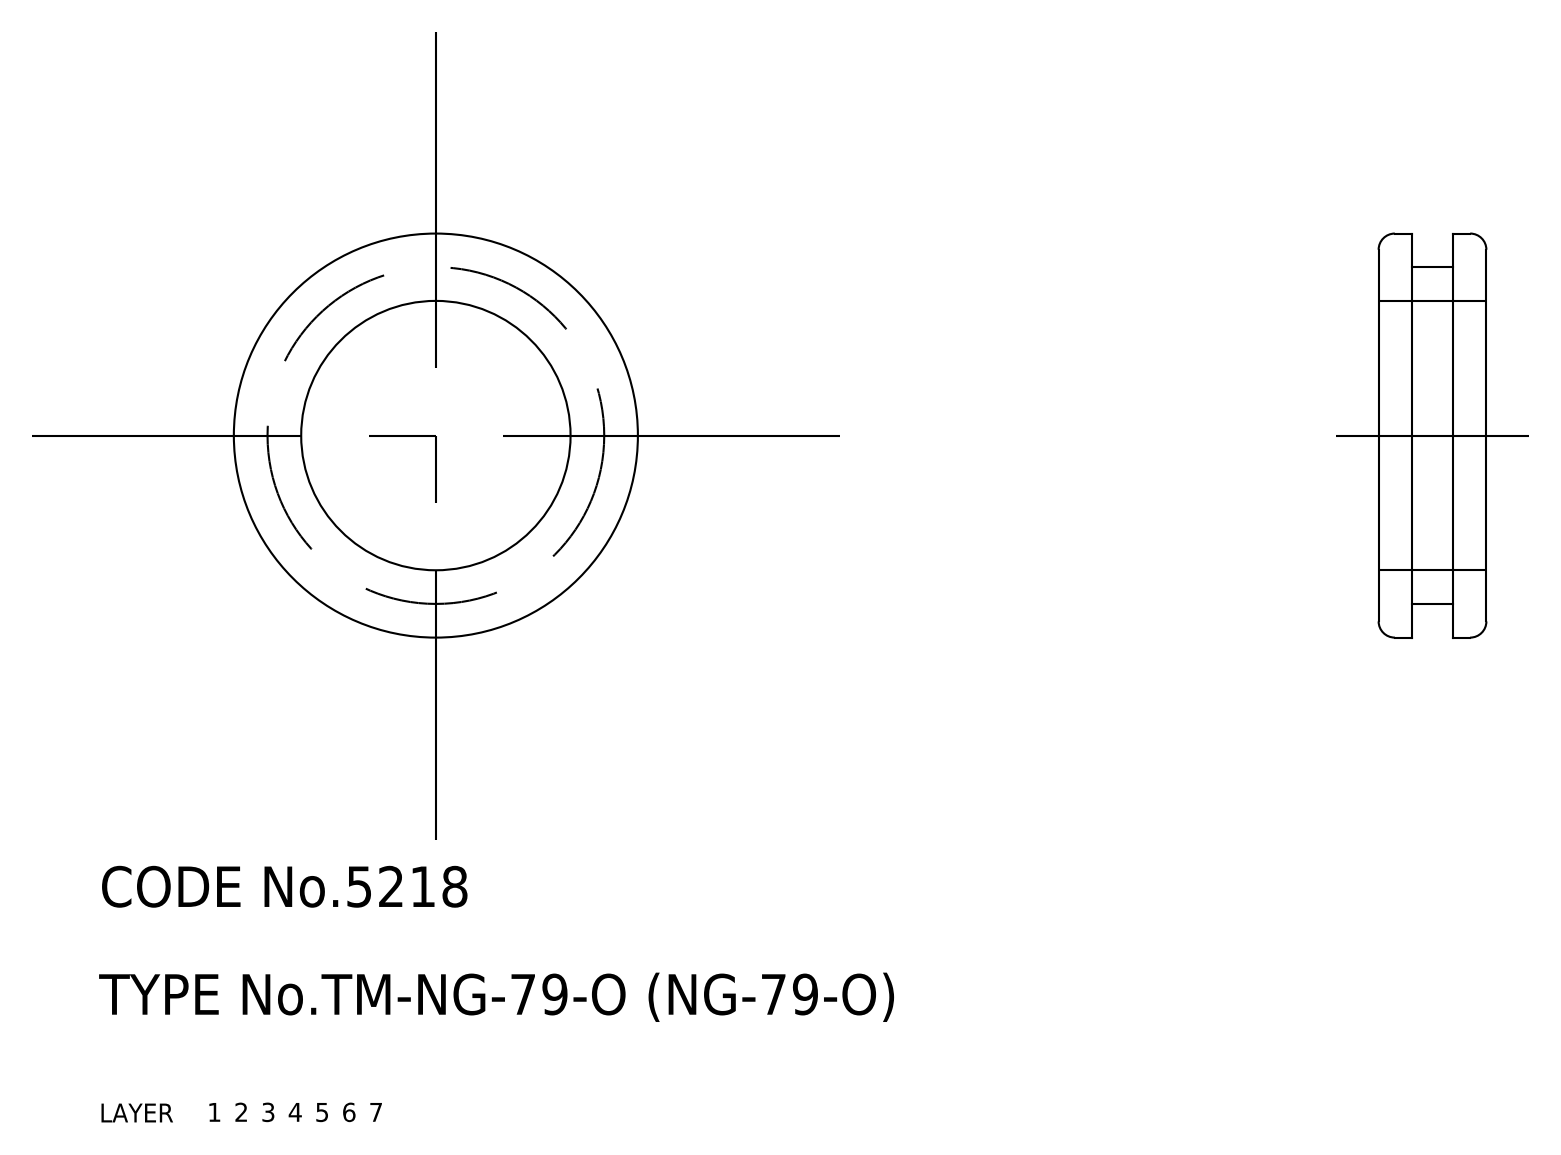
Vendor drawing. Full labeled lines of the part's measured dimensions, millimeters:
Part name (STEP PRODUCT): grommet
STEP written by: CADfix (AUTOMOTIVE_DESIGN)
Units: millimetres
Bodies: 1 solid, 16 faces (0 planar, 0 cylindrical, 16 other)
Overall size (bounding box): 30 × 30 × 8
Volume: 2 444 mm³ · Surface area: 2 330 mm²
